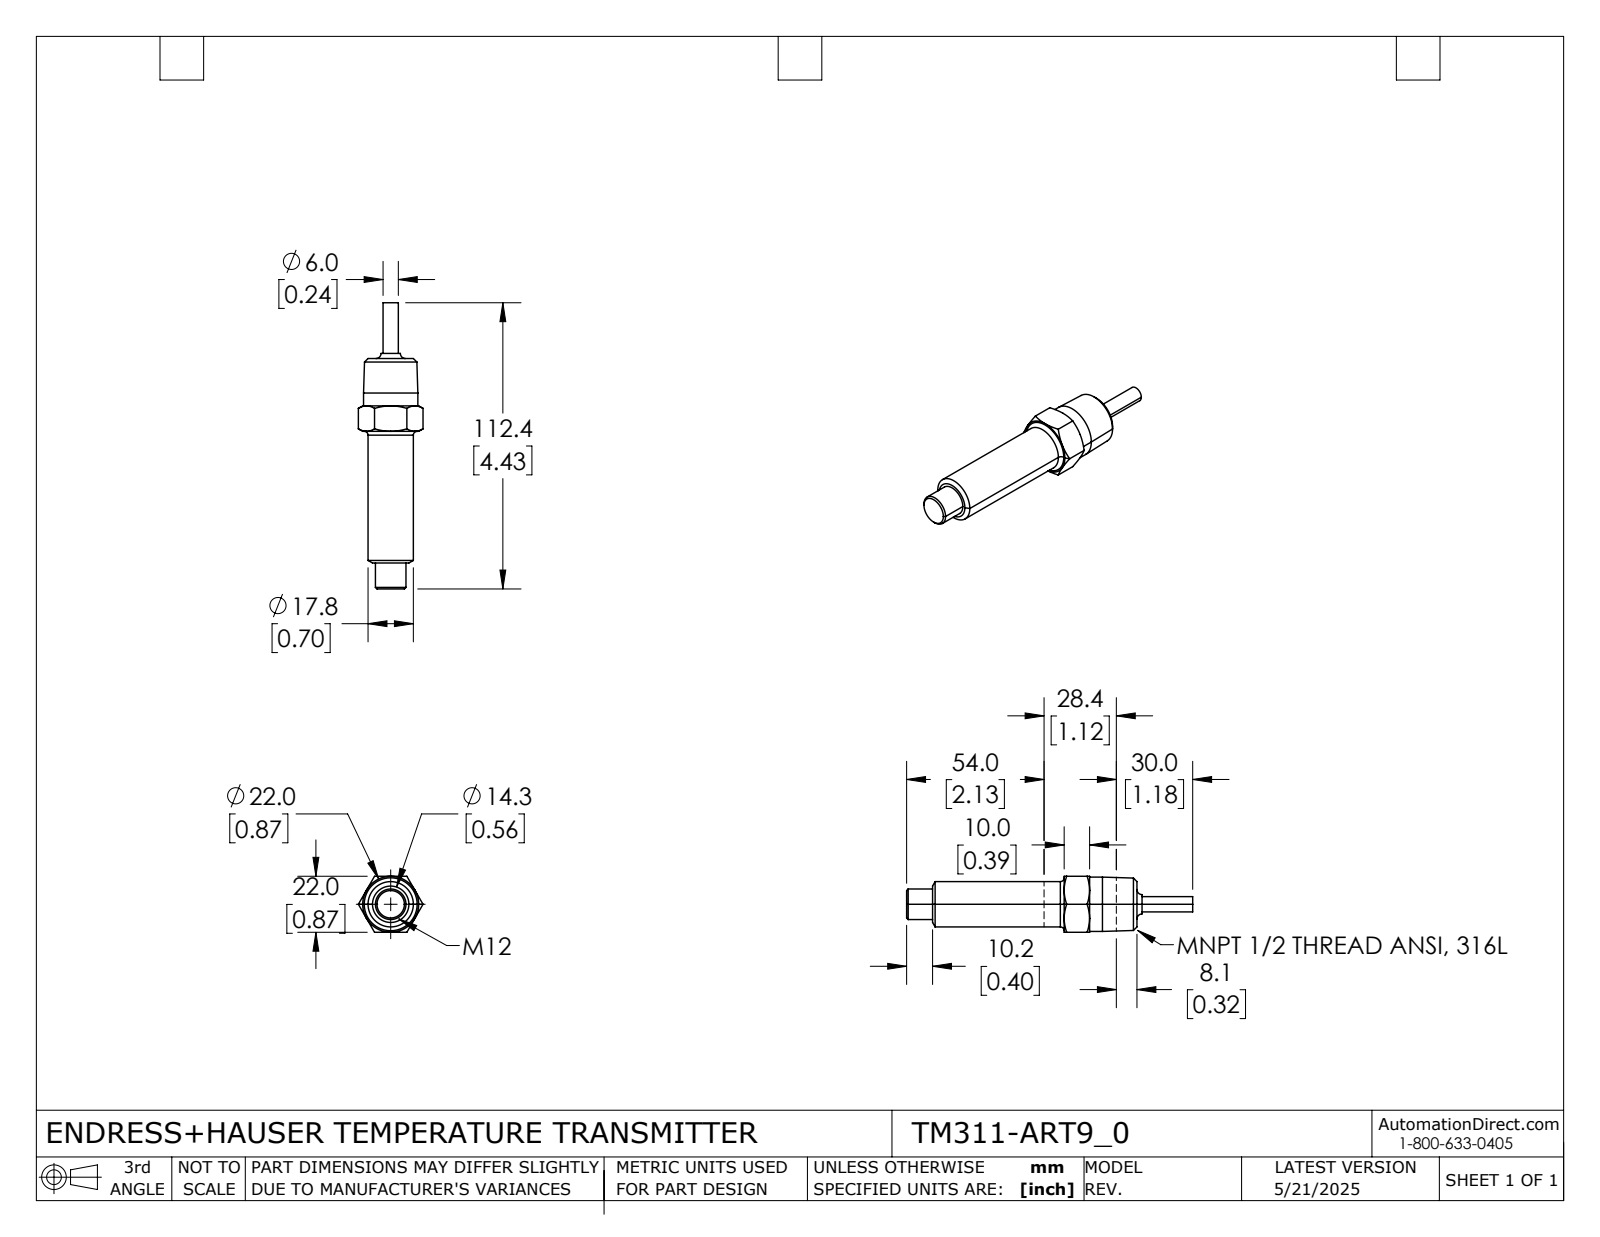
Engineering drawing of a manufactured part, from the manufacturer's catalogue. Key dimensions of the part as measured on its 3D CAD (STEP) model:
Part name (STEP PRODUCT): TM311-ART9_0
STEP written by: SolidWorks 2021 (AUTOMOTIVE_DESIGN)
Units: inches
Bodies: 1 solid, 49 faces (13 planar, 8 cylindrical, 28 other)
Overall size (bounding box): 4.425 × 1 × 0.866
Volume: 1.54 in³ · Surface area: 9.764 in²
Round bosses / shafts (diameter × count): ⌀0.84 ×1, ⌀0.701 ×1, ⌀0.472 ×1, ⌀0.236 ×1
Main face-to-face distances: 0.866, 3.563, 3.161, 0.402, 1.126, 2.035, 2.437, 0.862, 1.988, 4.024
